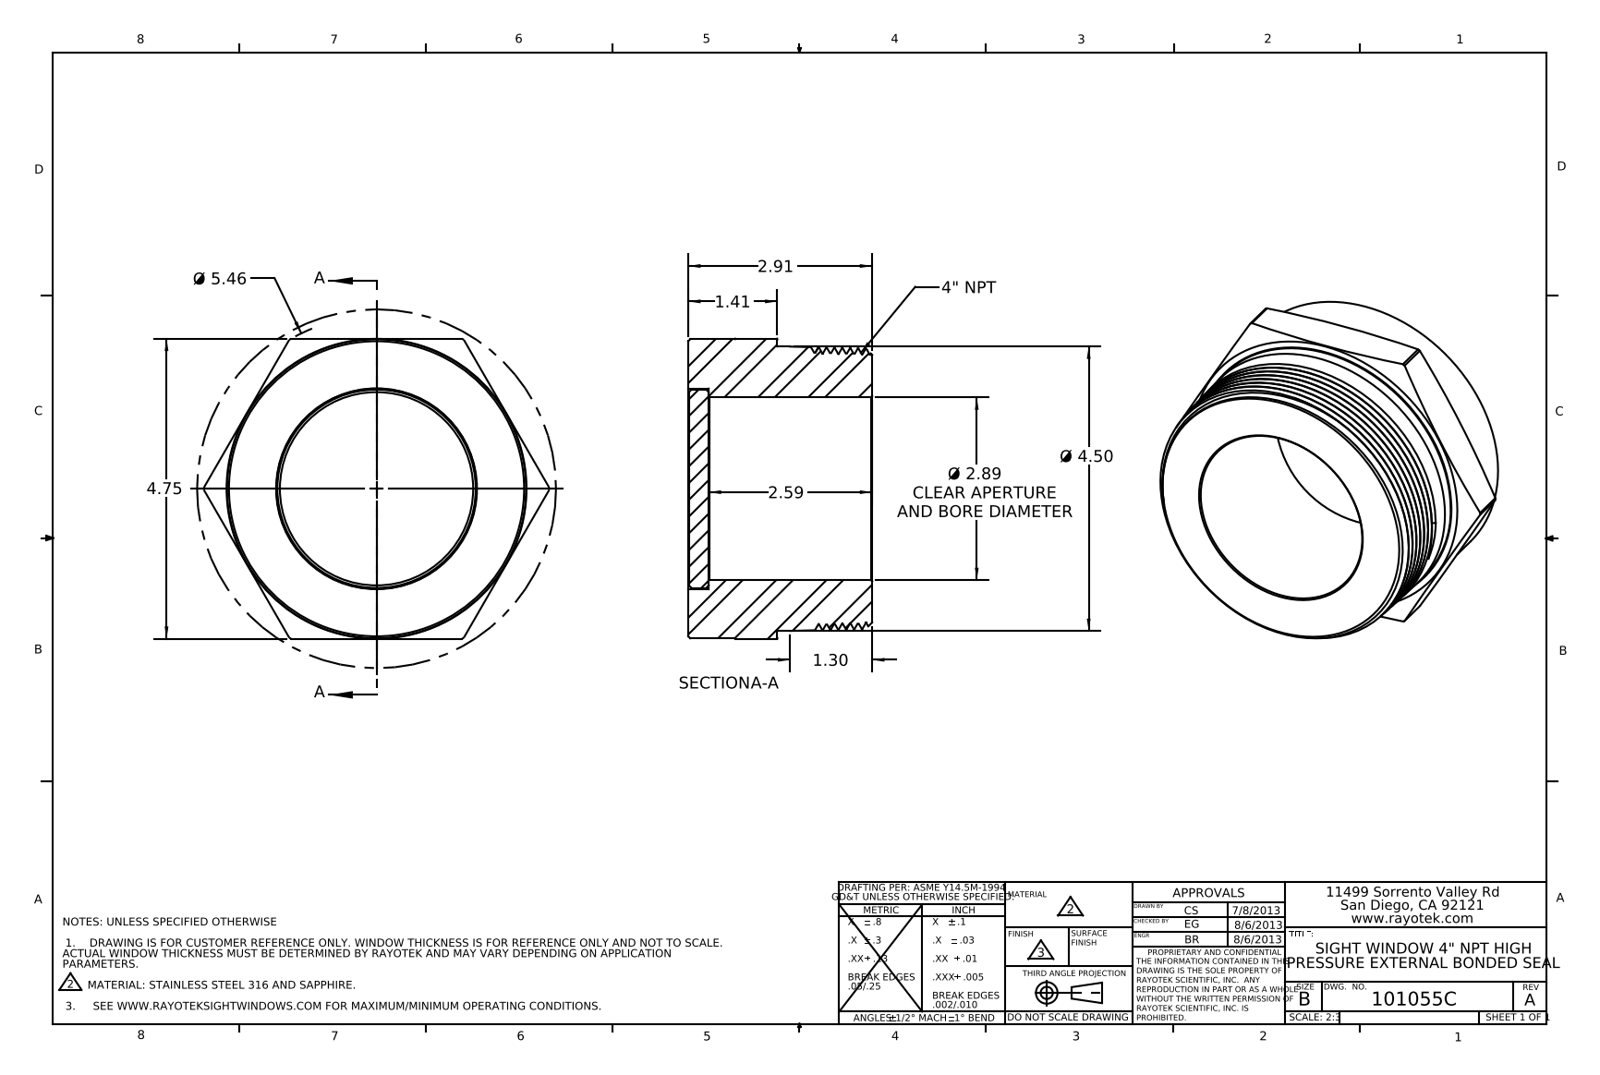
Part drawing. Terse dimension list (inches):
name: 101055; 402055; 403055
written by: SolidWorks 2012 (AUTOMOTIVE_DESIGN)
unit: in
bodies: 2 solids, 73 faces (15 planar, 17 cylindrical, 41 other)
size: 5.465 × 4.75 × 2.91
volume: 31.78 in³; area: 121.7 in²
holes: 1× ⌀2.89, 1× ⌀3.178
bosses: 1× ⌀4.73, 1× ⌀4.5, 1× ⌀3.138
rounds: 1× R2.732
face distances: 0.325, 0.315, 2.91, 2.9, 2.585, 4.75, 1.41, 1.4, 1.085, 1.5
